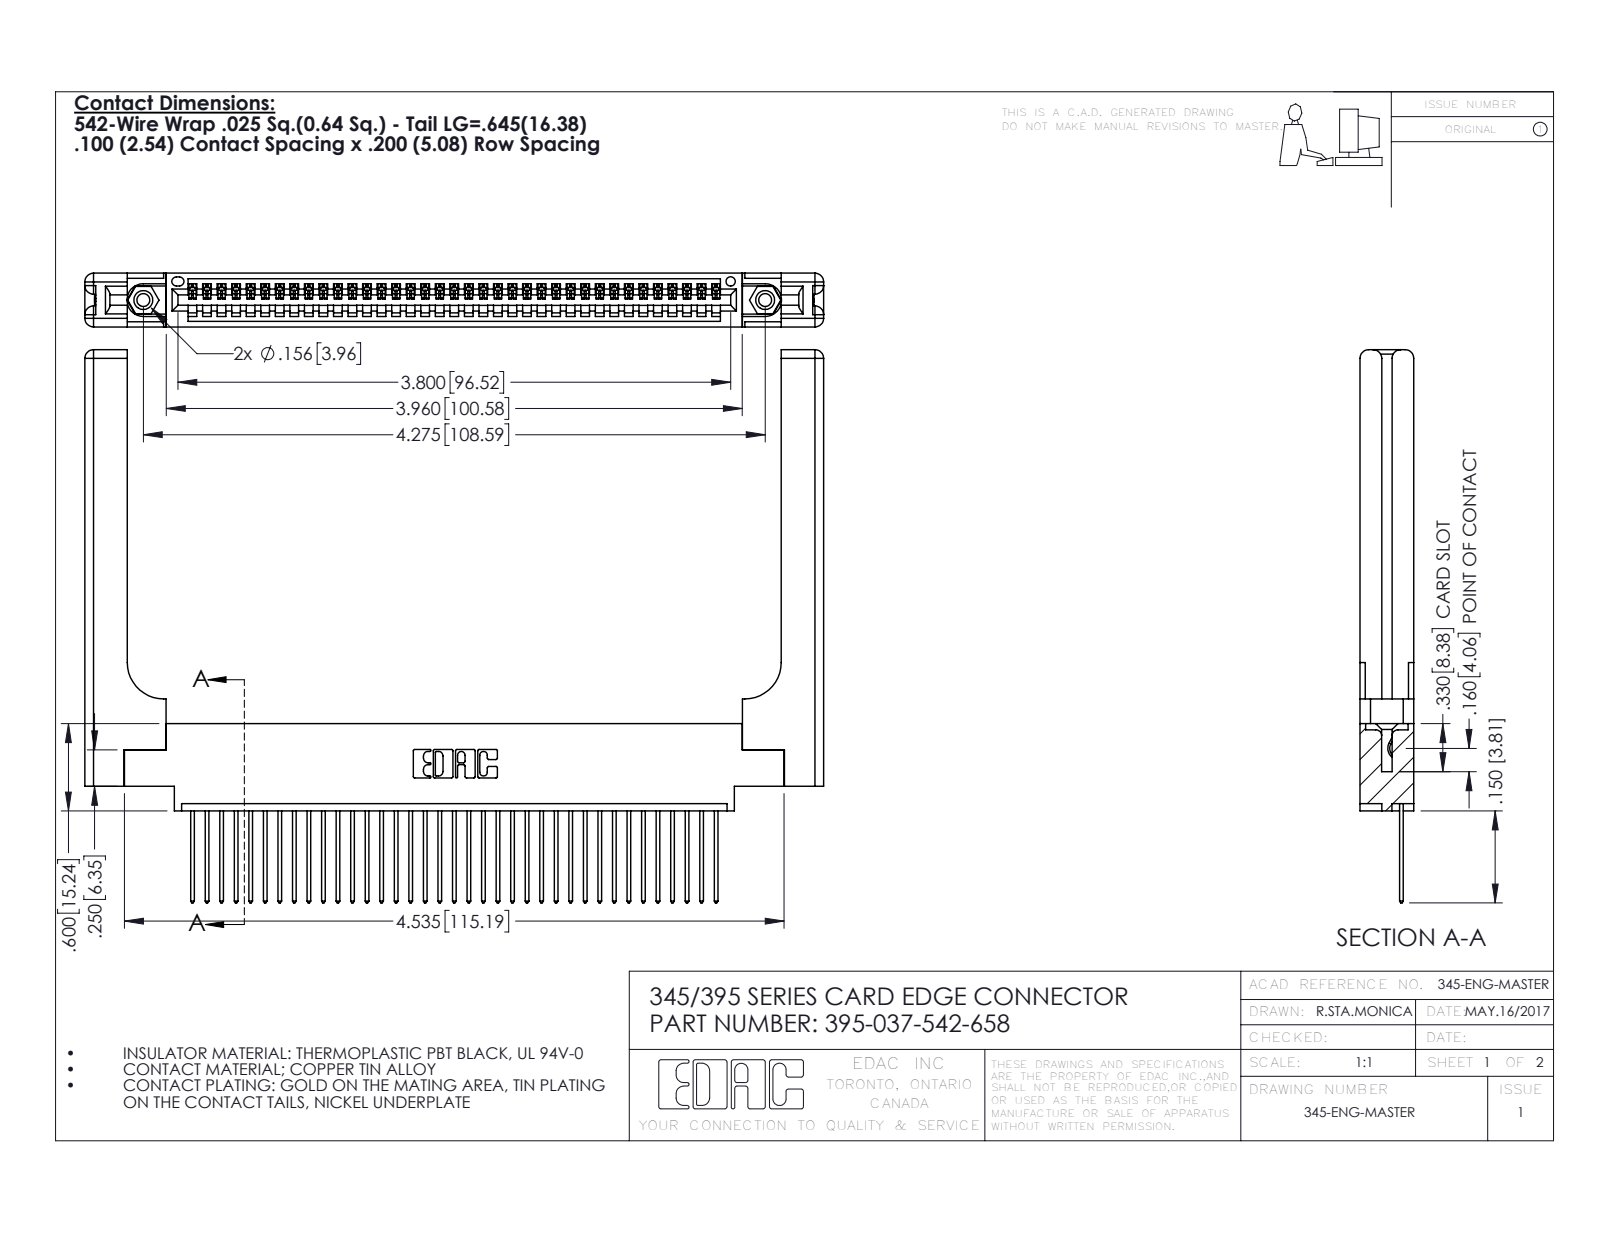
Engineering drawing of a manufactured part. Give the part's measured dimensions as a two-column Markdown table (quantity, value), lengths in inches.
| quantity | value |
| --- | --- |
| part name | 395-037-542-658; 345-220-058_345-220-058; 345 Part_0.170 Offset - 0.156 Dia-TH; 345-292-001_345-293-142 (+1 more) |
| STEP written by | SolidWorks 2016 (CONFIG_CONTROL_DESIGN) |
| units | inches |
| bodies | 42 solids, 2532 faces (1712 planar, 760 cylindrical, 60 other) |
| overall size | 5.079 × 3.802 × 0.37 |
| volume | 1.262 in³ |
| surface area | 34.21 in² |
| round holes (diameter × count) | 0.089 × 2, 0.125 × 2, 0.156 × 2, 0.064 × 1 |
| round bosses / shafts (diameter × count) | 0.155 × 2 |
| partial cylindrical surfaces (radius × count) | 0.006 × 74, 0.01 × 74, 0.01 × 22, 0.06 × 16, 0.007 × 6, 0.031 × 6, 0.026 × 3, 0.03 × 2 |
| main face-to-face distances | 0.37, 0.072, 0.298, 0.098, 0.272, 0.025, 0.2, 0.148, 0.15, 0.225 |
| hole center spacings | 0.27, 4.039, 4.275 |
